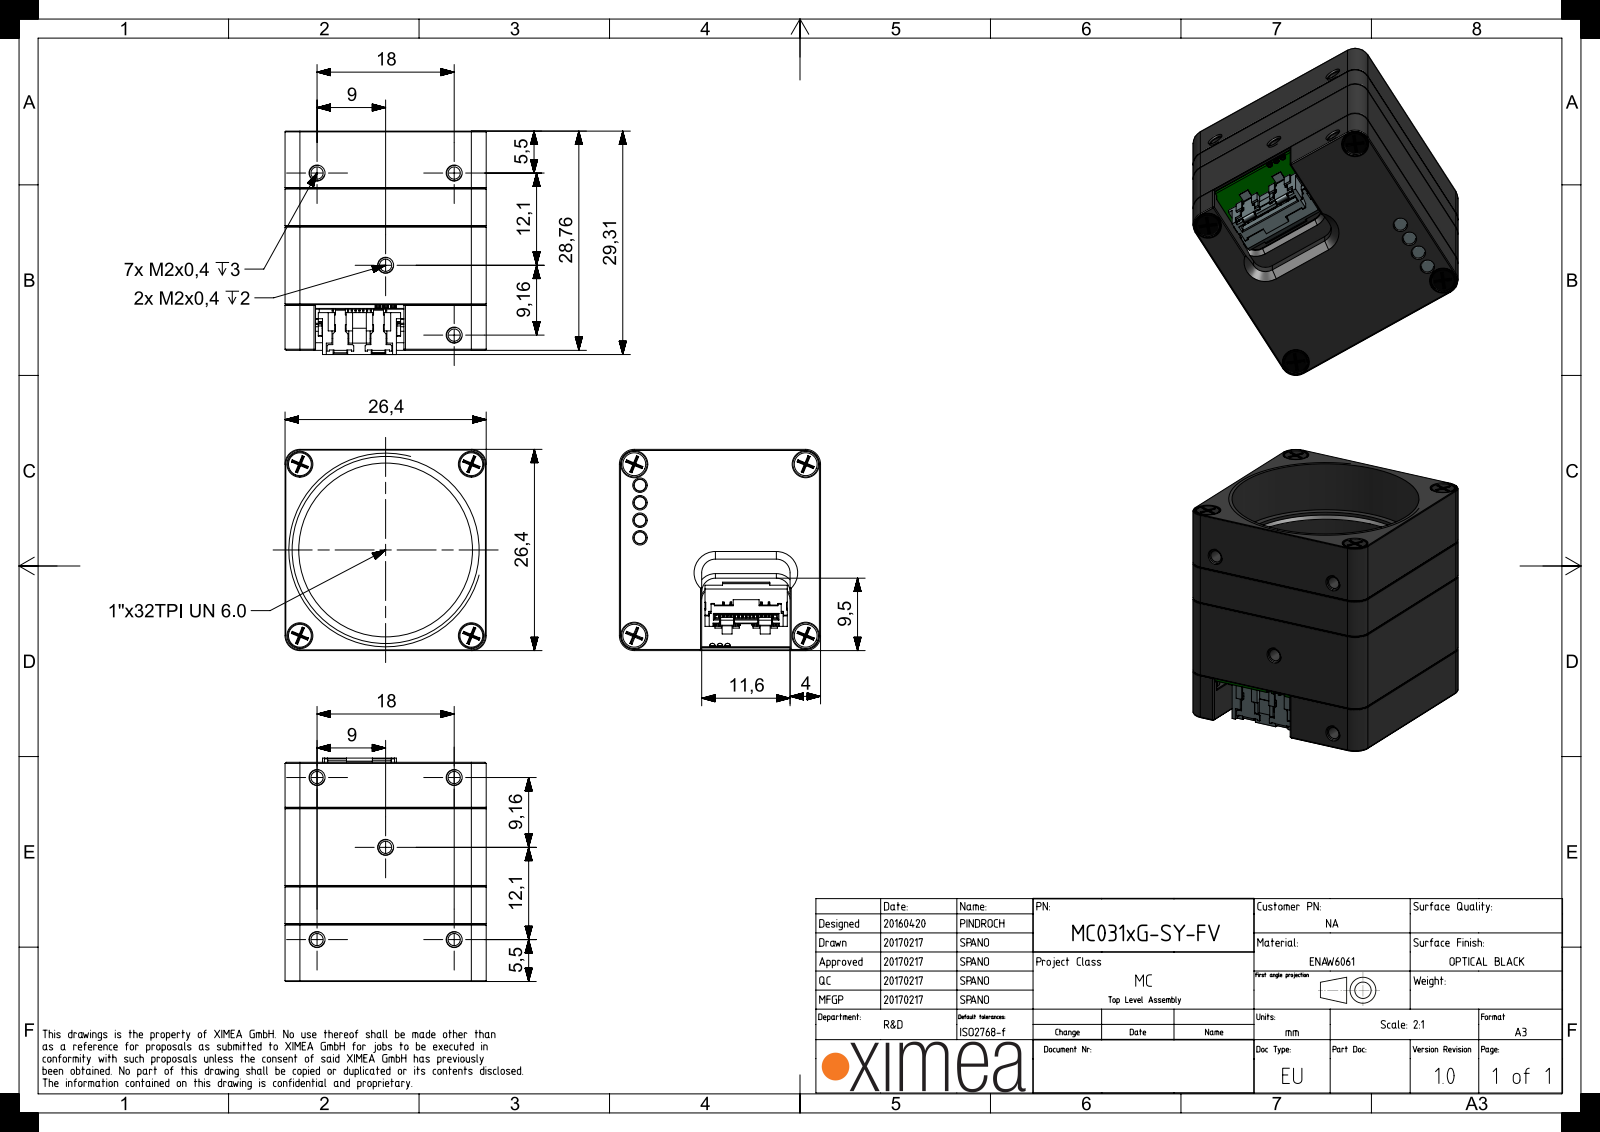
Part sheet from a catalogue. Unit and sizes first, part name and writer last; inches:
Units: inches
Overall size (bounding box): 1.154 × 1.039 × 1.039
Round holes (diameter × count): ⌀0.063 ×13, ⌀0.039 ×4, ⌀0.071 ×4, ⌀0.079 ×4, ⌀0.083 ×4, ⌀0.118 ×4, ⌀0.126 ×4, ⌀0.132 ×4, ⌀0.051 ×2, ⌀0.073 ×1, ⌀0.073 ×1, ⌀0.157 ×1
Round bosses / shafts (diameter × count): ⌀0.075 ×4, ⌀0.064 ×4, ⌀0.033 ×4, ⌀0.118 ×2, ⌀0.063 ×2, ⌀0.984 ×1, ⌀0.85 ×1
Partial cylindrical surfaces — rounded edges, fillets, slot ends (radius × count): R0.039 ×26, R0.013 ×16, R0.006 ×14, R0.004 ×12, R0.015 ×12, R0.059 ×12, R0.051 ×8, R0.008 ×7
Main face-to-face distances: 0.039, 0.138, 1.039, 0.27, 0.304, 0.165, 0.178, 0.447, 0.408, 0.266
Hole centre spacings: 0.15, 0.508, 0.626, 0.739, 0.869, 0.886, 1.131, 0.091
Volume: 0.602 in³ · Surface area: 26.79 in²
Bodies: 32 solids, 7154 faces (4910 planar, 1953 cylindrical, 291 other)
Part name (STEP PRODUCT): MECH-O-RING-22X1-VI370; MT031xG-PR-SENSOR-PCA; FLT-BK7-AR2X-D25; SROB-M1.6x3-SLOT-STNLS (+8 more)
STEP written by: SIEMENS PLM Software NX 1907 (AUTOMOTIVE_DESIGN)
